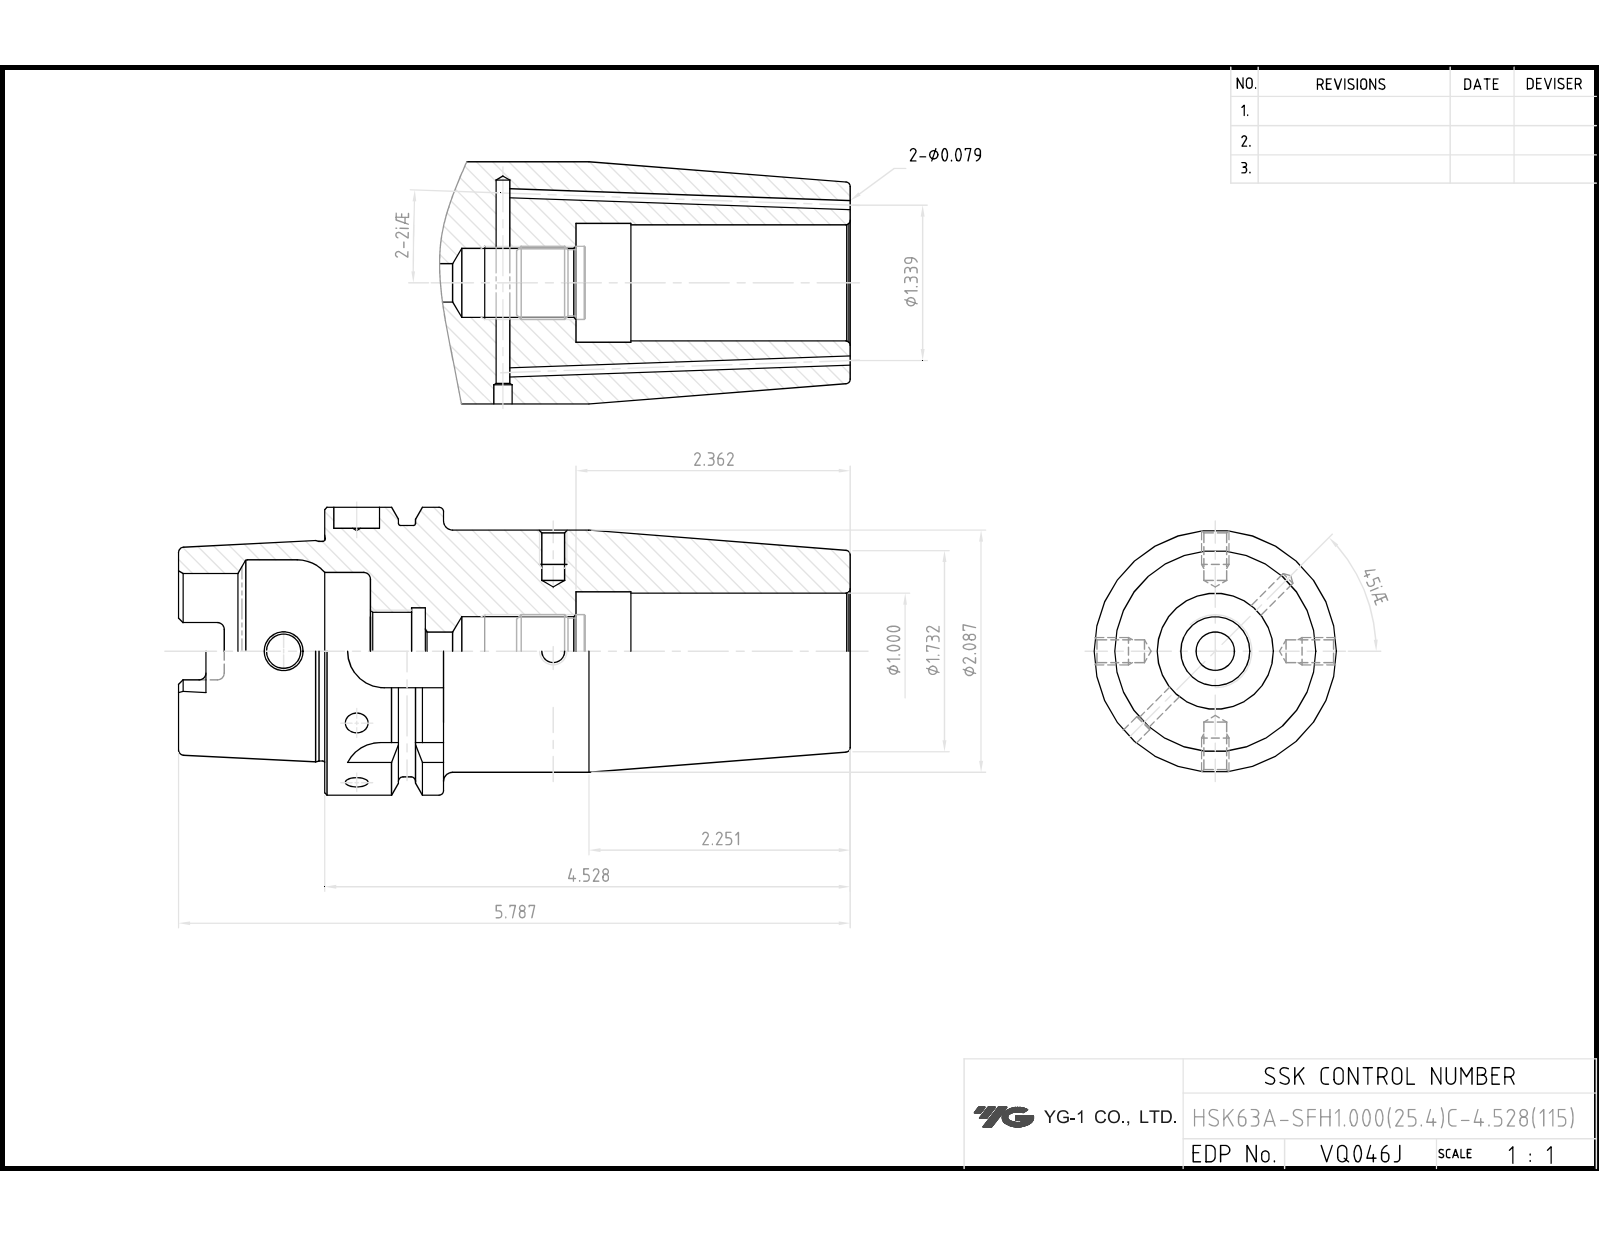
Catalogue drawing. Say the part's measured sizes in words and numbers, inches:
The part is named "VQ046J-HSK63A-SFH1_0C-4_53". Its 3-D file was written by "PRO/ENGINEER BY PARAMETRIC TECHNOLOGY CORPORATION, 2012130 (CONFIG_CONTROL_DESIGN)". It is 1 solid with 204 faces: 59 planar, 59 cylindrical and 86 other. Overall it measures 5.788 by 2.48 by 2.48 inches. Its volume is 13.33 cubic inches and its surface area 66.04 square inches. Round holes: 2 of diameter 0.197, 1 of diameter 0.295, 1 of diameter 0.327, 1 of diameter 0.394, 1 of diameter 0.592, 1 of diameter 0.669, 1 of diameter 0.709, 1 of diameter 0.748, 1 of diameter 1.012, 1 of diameter 1.028, 1 of diameter 1.339, 1 of diameter 1.358. Round bosses or shafts: 1 of diameter 2.48, 1 of diameter 2.165, 1 of diameter 2.087, 1 of diameter 1.891. Partial cylindrical surfaces (rounded edges, fillets, slot ends): 6 of radius 0.059, 4 of radius 0.113, 4 of radius 0.315. The main face-to-face distances are 4.528, 0.394, 4.134, 1.26, 1.024, 0.63, 1.654, 5.788, 3.504, 2.283. The hole center spacings are 1.693, 2.323.
